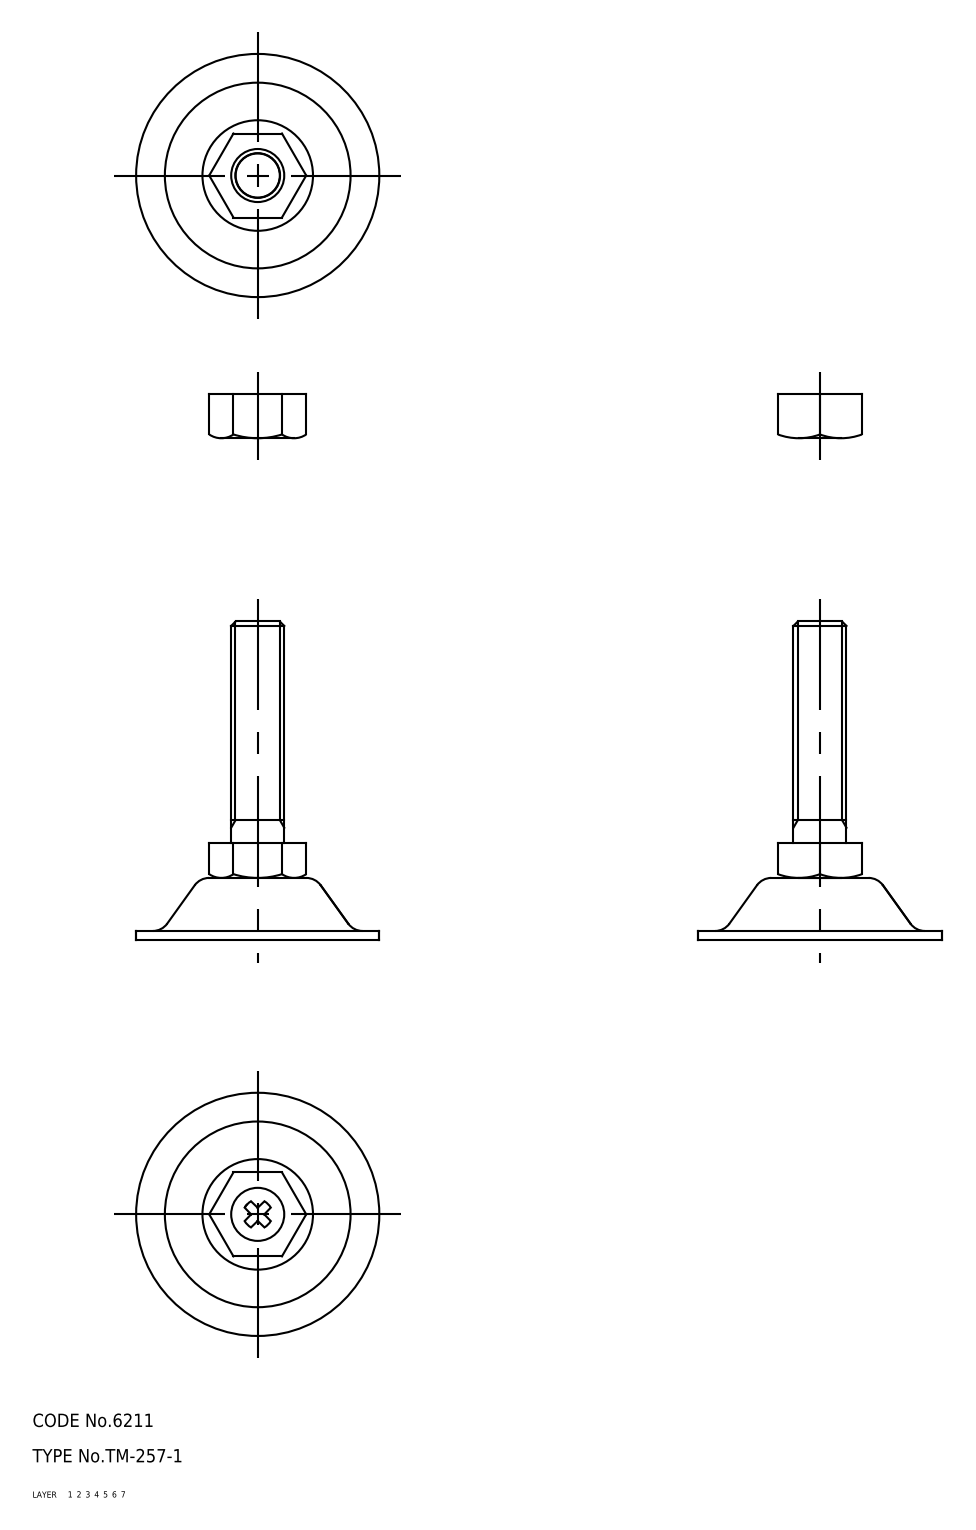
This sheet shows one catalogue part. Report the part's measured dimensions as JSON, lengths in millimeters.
{"part_name": "nut; foot; bolt; TM_257_1_9443_36", "step_written_by": "CADfix (AUTOMOTIVE_DESIGN)", "units": "millimeters", "bodies": {"solids": 4, "faces": 91, "planar": 0, "cylindrical": 0, "other": 91}, "overall_size": [72, 55, 55], "volume_mm3": 19165, "surface_area_mm2": 12466}
